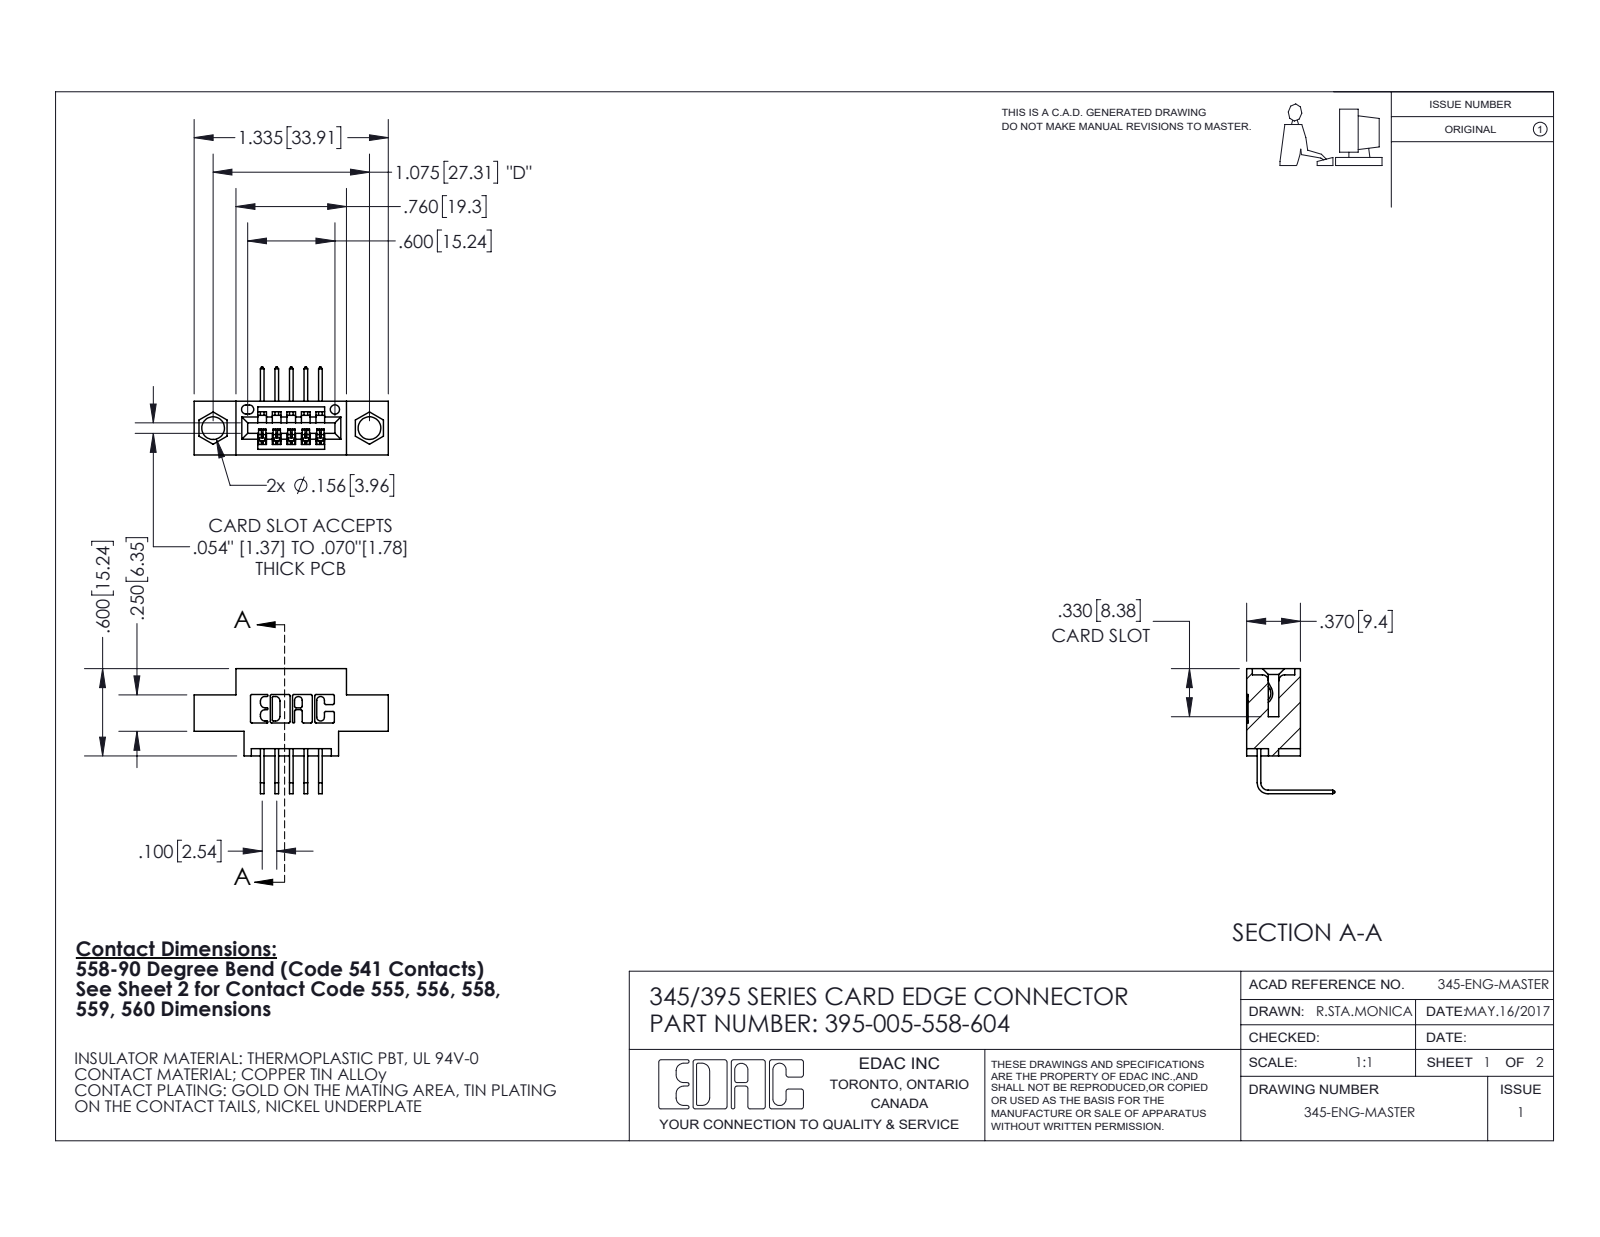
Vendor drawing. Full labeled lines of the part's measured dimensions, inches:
Part name (STEP PRODUCT): 345-292-001_558 Tail - 2; 345 Part_0.170 Offset - 0.156 Dia-TI; 395-005-558-604
STEP written by: SolidWorks 2020 (CONFIG_CONTROL_DESIGN)
Units: inches
Bodies: 6 solids, 444 faces (308 planar, 136 cylindrical, 0 other)
Overall size (bounding box): 1.335 × 0.859 × 0.605
Volume: 0.166 in³ · Surface area: 4.917 in²
Round holes (diameter × count): ⌀0.156 ×2, ⌀0.064 ×1
Partial cylindrical surfaces — rounded edges, fillets, slot ends (radius × count): R0.01 ×22, R0.006 ×10, R0.007 ×6, R0.031 ×6, R0.026 ×3, R0.031 ×2, R0.04 ×2, R0.014 ×1
Main face-to-face distances: 0.37, 0.2, 0.1, 0.072, 0.298, 0.025, 0.098, 0.272, 0.25, 0.06
Hole centre spacings: 0.27, 0.847, 1.075
